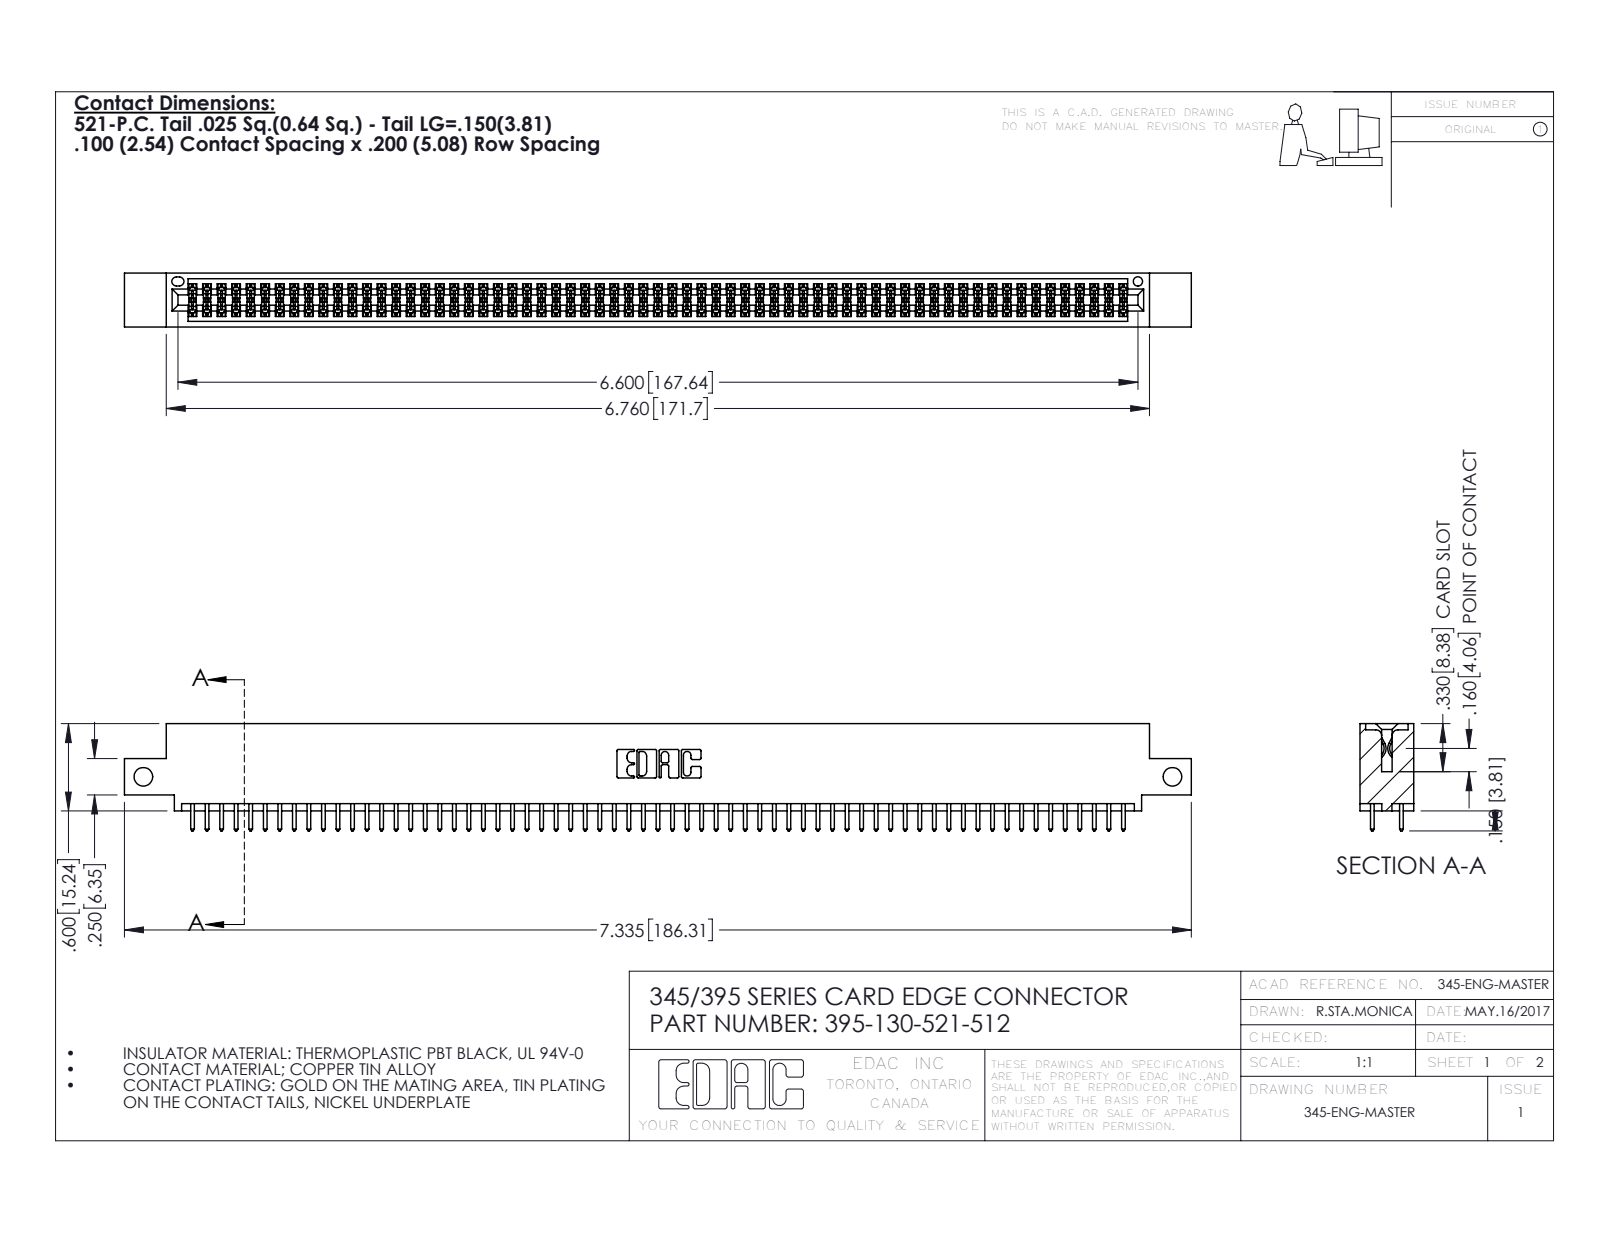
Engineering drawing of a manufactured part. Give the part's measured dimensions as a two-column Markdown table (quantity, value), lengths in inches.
| quantity | value |
| --- | --- |
| part name | 345-292-001_345-293-121; 345 Part_0.110 Offset - Side Mount; 395-130-521-512 |
| STEP written by | SolidWorks 2016 (CONFIG_CONTROL_DESIGN) |
| units | inches |
| bodies | 131 solids, 6630 faces (4374 planar, 2256 cylindrical, 0 other) |
| overall size | 7.335 × 0.737 × 0.37 |
| volume | 1.104 in³ |
| surface area | 41.55 in² |
| round holes (diameter × count) | 0.128 × 2, 0.064 × 1 |
| partial cylindrical surfaces (radius × count) | 0.006 × 195, 0.01 × 130, 0.01 × 22, 0.007 × 6, 0.031 × 6, 0.026 × 3, 0.014 × 2, 0.019 × 2 |
| main face-to-face distances | 0.298, 0.072, 0.2, 0.098, 0.272, 0.025, 0.37, 0.225, 0.175, 0.149 |
| hole center spacings | 7.075 |
